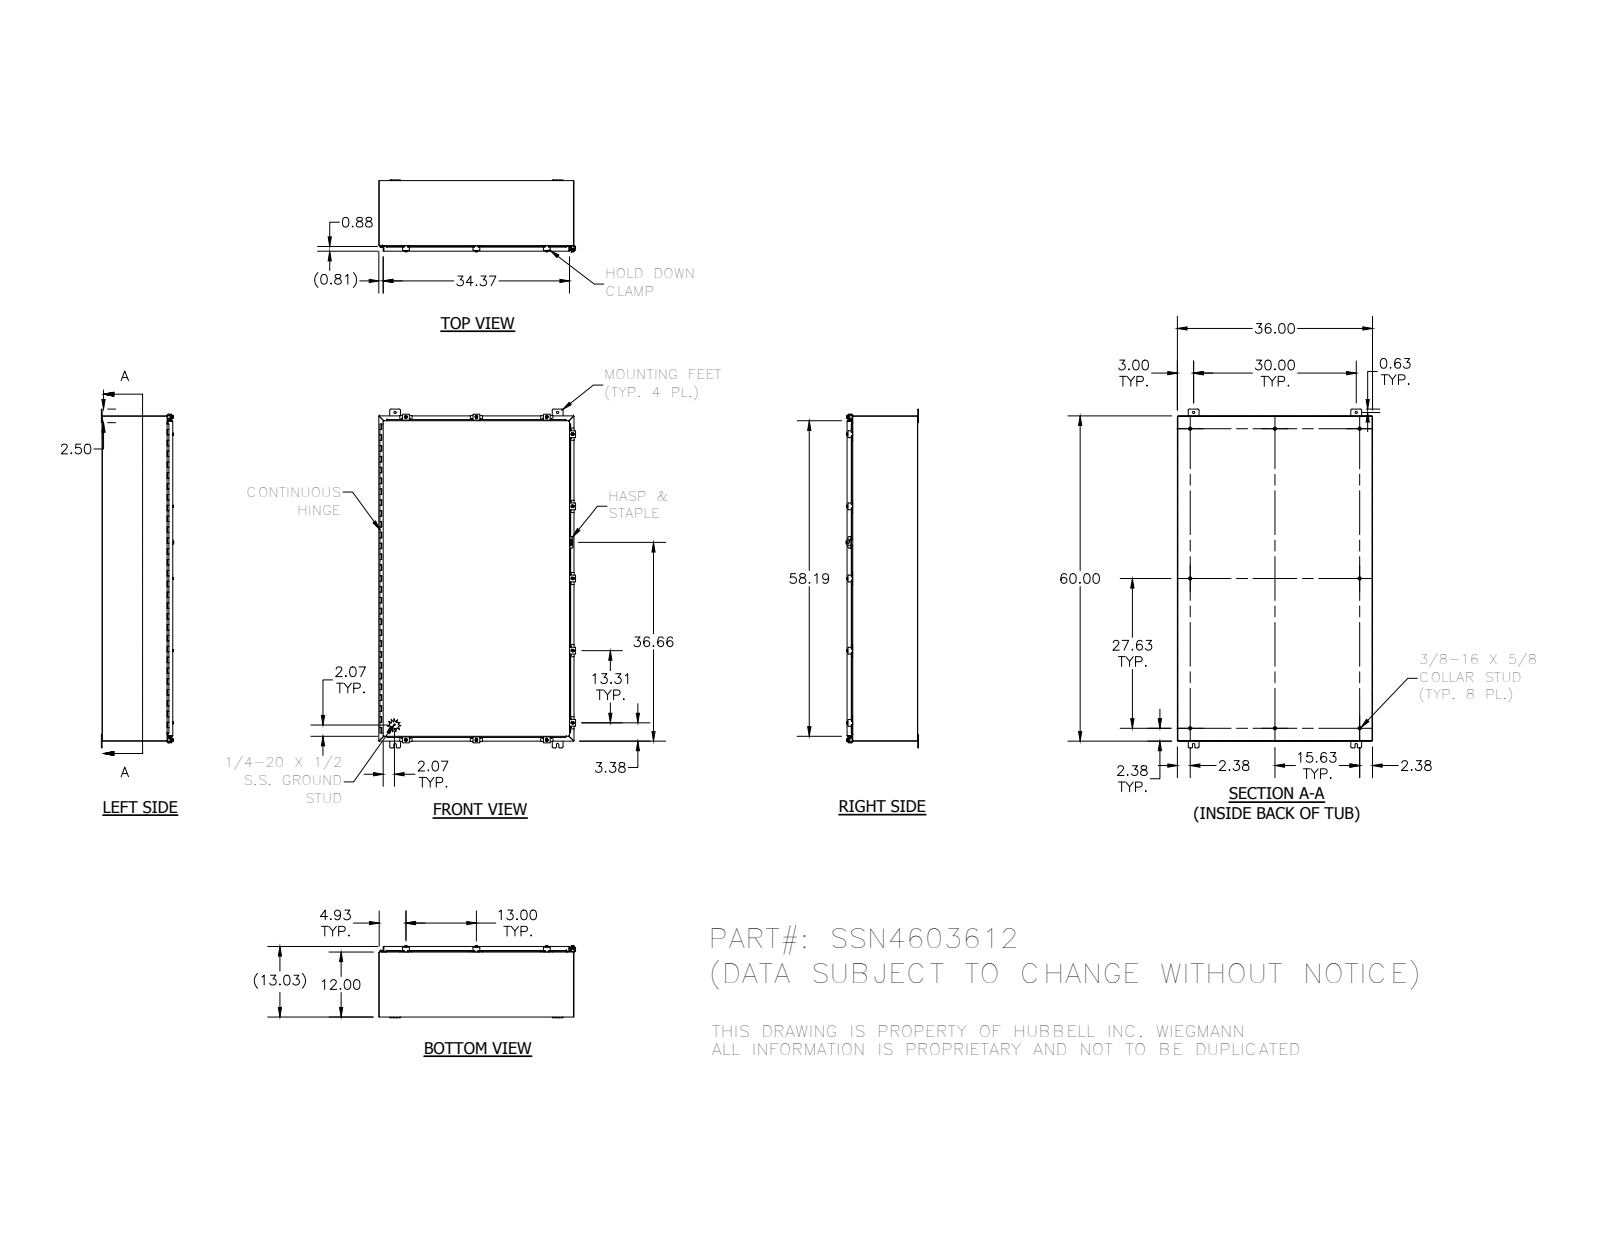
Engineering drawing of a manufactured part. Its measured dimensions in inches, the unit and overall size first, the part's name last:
Units: inches
Overall size (bounding box): 62.5 × 36.311 × 13.355
Round holes (diameter × count): ⌀0.11 ×25, ⌀0.211 ×11, ⌀0.281 ×11, ⌀0.3 ×11, ⌀0.438 ×4, ⌀0.125 ×1, ⌀0.156 ×1, ⌀0.5 ×1
Round bosses / shafts (diameter × count): ⌀0.25 ×13, ⌀0.52 ×11, ⌀0.5 ×11, ⌀0.35 ×11, ⌀0.625 ×8, ⌀0.33 ×8, ⌀0.337 ×1, ⌀0.12 ×1
Partial cylindrical surfaces — rounded edges, fillets, slot ends (radius × count): R0.03 ×129, R0.125 ×43, R0.25 ×39, R0.141 ×22, R0.031 ×21, R0.105 ×21, R0.062 ×20, R0.1 ×16
Main face-to-face distances: 0.074, 12.959, 12.885, 13.033, 35.926, 59.926, 35.852, 36, 11.926, 1.033
Hole centre spacings: 0.876, 13, 59.294, 12.192, 13.817, 60.377, 60.529, 60.877
Volume: 557 in³ · Surface area: 14 811 in²
Bodies: 78 solids, 3218 faces (1272 planar, 1399 cylindrical, 547 other)
Part name (STEP PRODUCT): 30824; 32874-60; 34871; 32874-60L (+8 more)
STEP written by: SolidWorks 2014 (AUTOMOTIVE_DESIGN)
